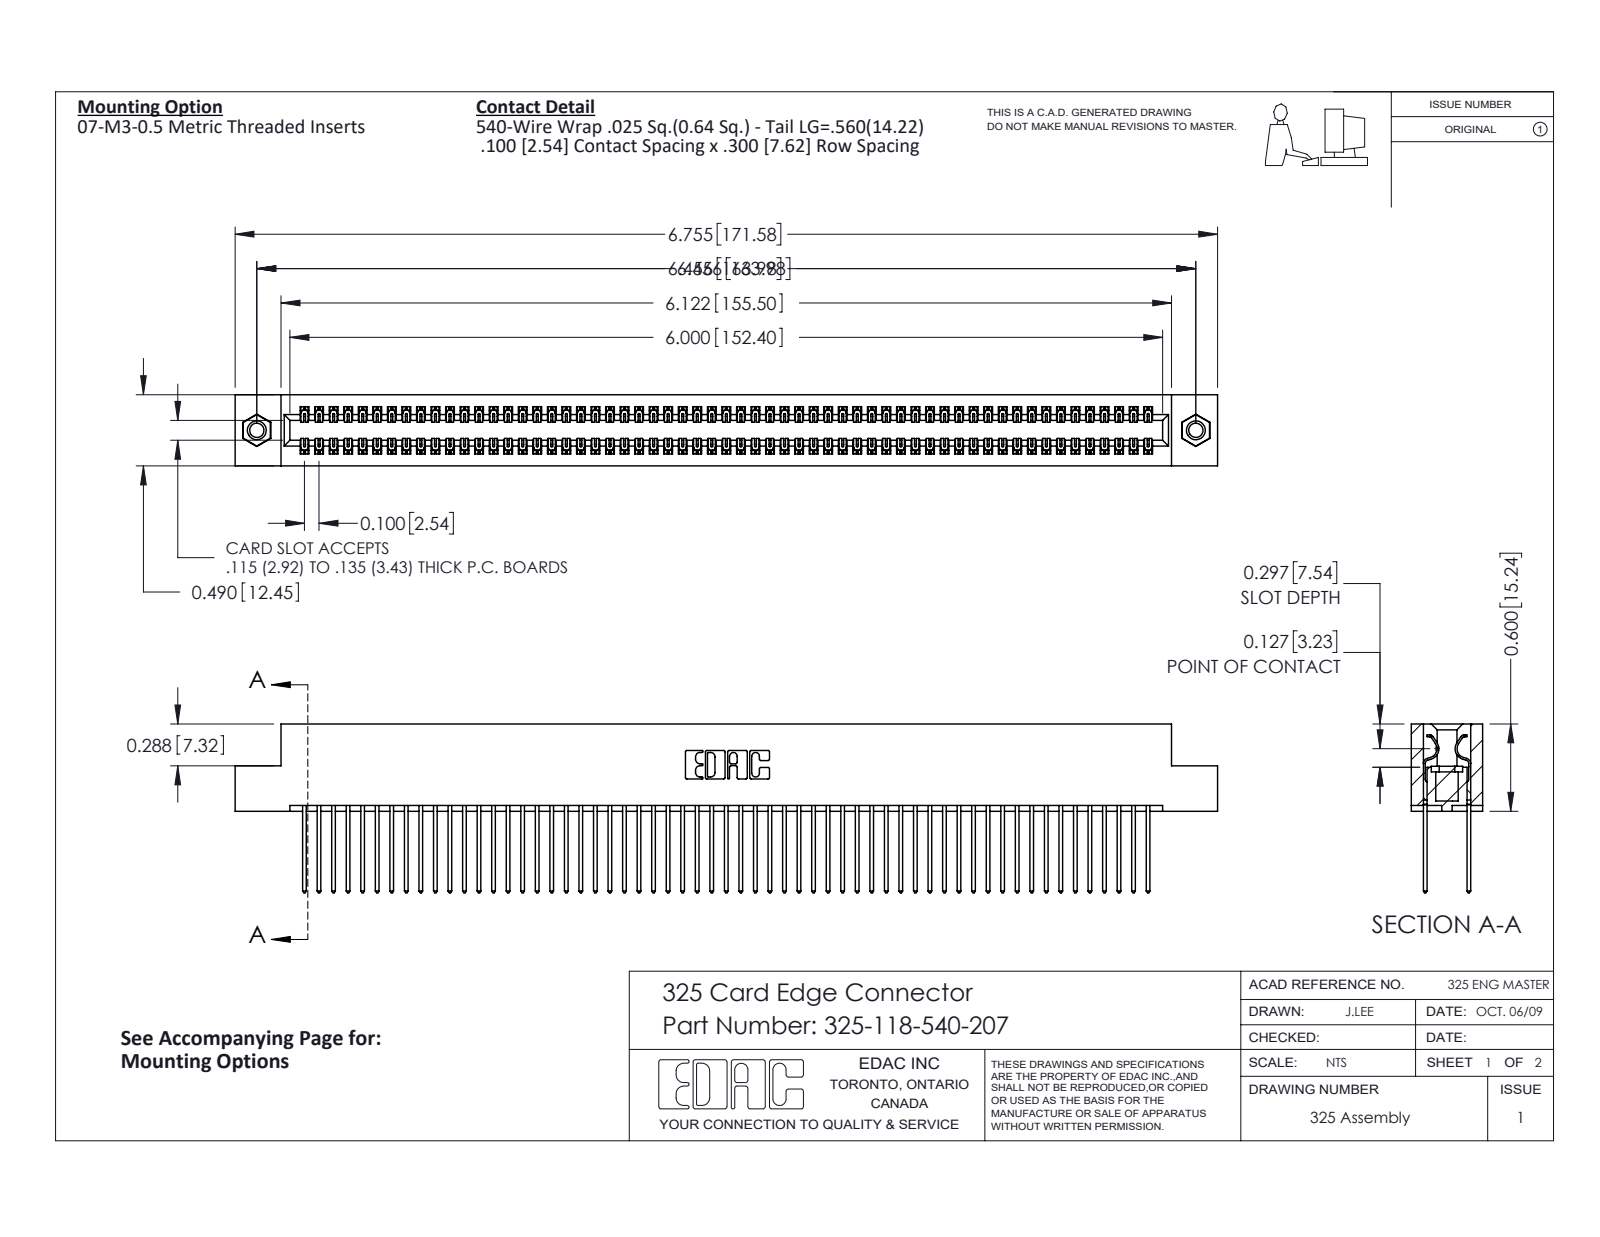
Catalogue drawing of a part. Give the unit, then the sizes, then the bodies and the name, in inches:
Units: inches
Overall size (bounding box): 6.755 × 1.16 × 0.49
Round holes (diameter × count): ⌀0.098 ×2, ⌀0.125 ×2, ⌀0.16 ×2
Round bosses / shafts (diameter × count): ⌀0.155 ×2
Partial cylindrical surfaces — rounded edges, fillets, slot ends (radius × count): R0.006 ×177, R0.01 ×118, R0.01 ×22, R0.007 ×6, R0.031 ×6, R0.026 ×3, R0.014 ×2, R0.022 ×2
Main face-to-face distances: 0.083, 0.407, 0.3, 0.107, 0.383, 0.025, 0.325, 0.49, 0.275, 0.56
Hole centre spacings: 6.456
Volume: 1.387 in³ · Surface area: 46.62 in²
Bodies: 121 solids, 6310 faces (4350 planar, 1944 cylindrical, 16 other)
Part name (STEP PRODUCT): 325-118-540-207; 325-292-001_325-293-140; 345-250-001_345-250-005-103; 325 Part_TI
STEP written by: SolidWorks 2016 (CONFIG_CONTROL_DESIGN)
